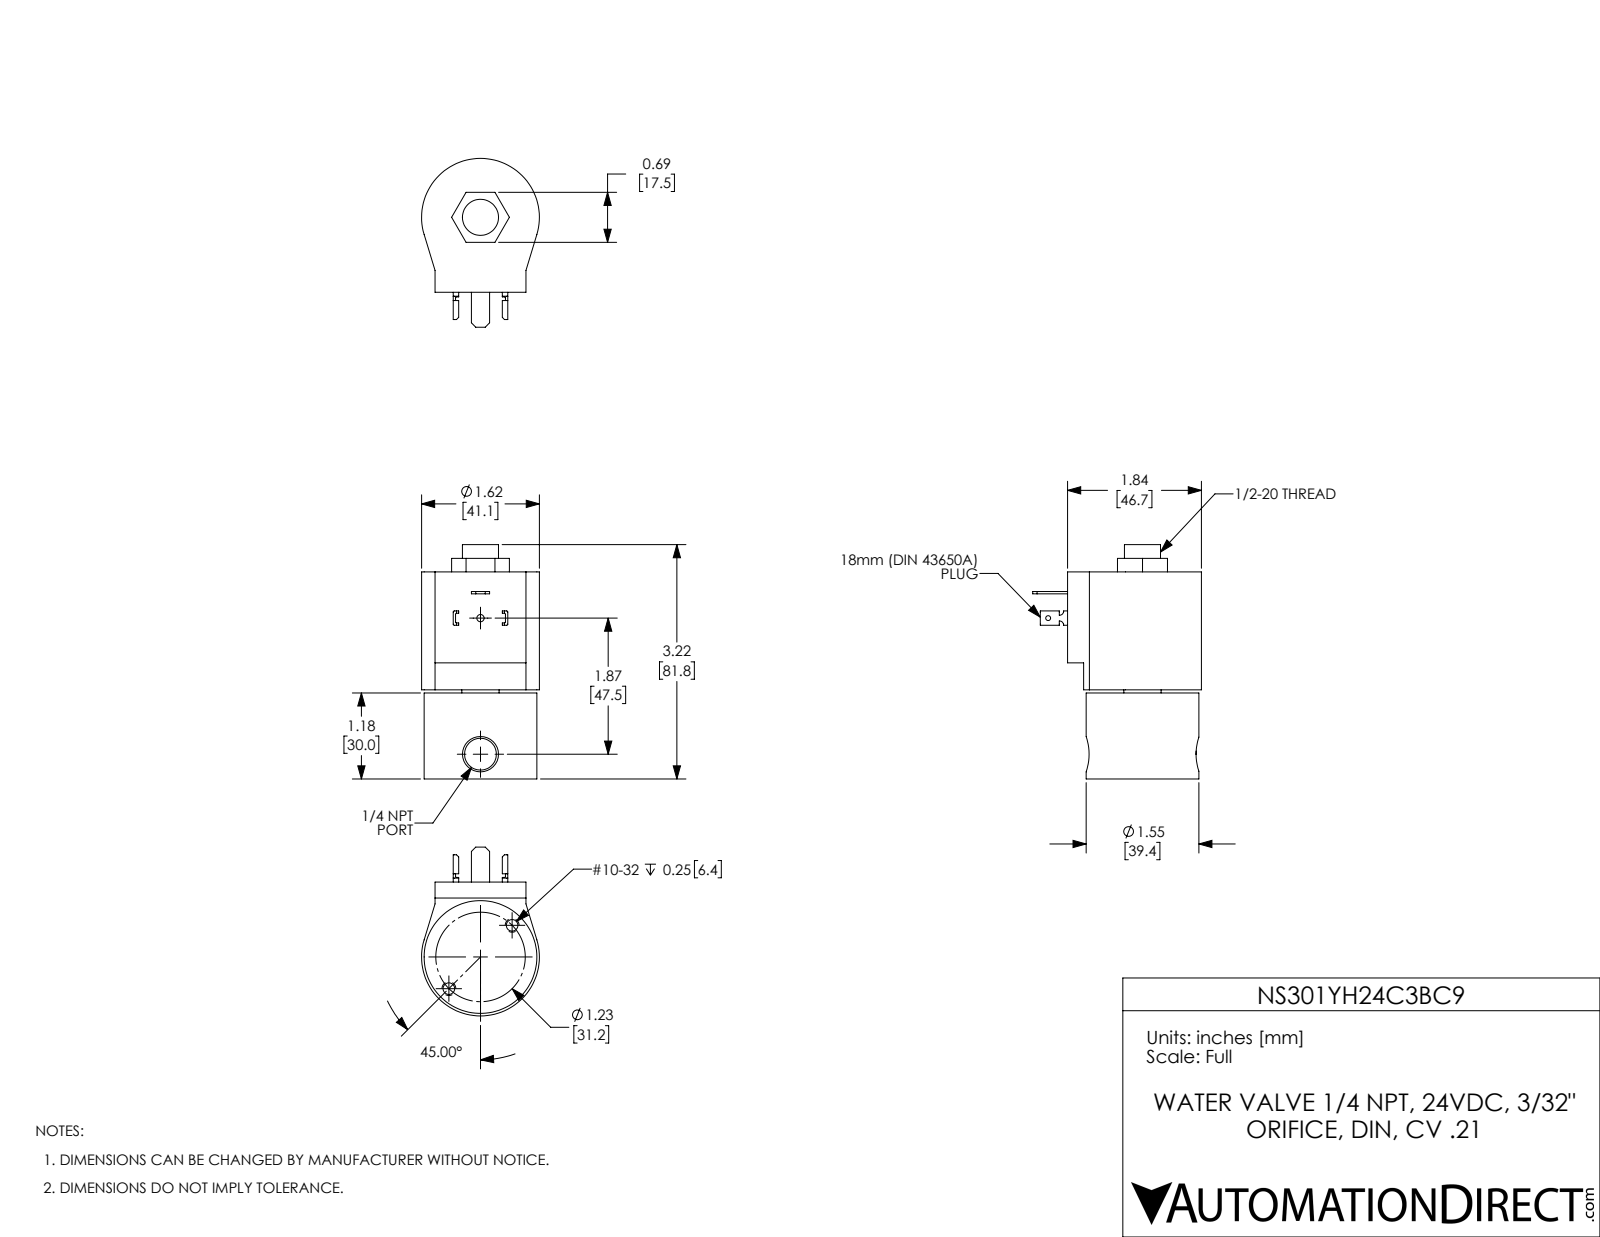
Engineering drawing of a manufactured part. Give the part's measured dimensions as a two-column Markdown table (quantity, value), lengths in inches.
| quantity | value |
| --- | --- |
| part name | NS301YH16C3BC9 |
| STEP written by | SolidWorks 2024 (CONFIG_CONTROL_DESIGN) |
| units | inches |
| bodies | 6 solids, 130 faces (73 planar, 49 cylindrical, 8 other) |
| overall size | 3.22 × 2.32 × 1.62 |
| volume | 6.042 in³ |
| surface area | 33.19 in² |
| round holes (diameter × count) | 0.159 × 2, 0.067 × 1, 0.1 × 1, 0.437 × 1, 0.496 × 1, 0.512 × 1, 1.155 × 1 |
| round bosses / shafts (diameter × count) | 1.55 × 1 |
| partial cylindrical surfaces (radius × count) | 0.015 × 8, 0.06 × 2, 0.81 × 1 |
| main face-to-face distances | 2.845, 1.182, 1.663, 1.225, 0.043, 1.62, 1.287, 0.106, 0.062, 1.558 |
| hole center spacings | 0.615, 1.23, 1.87 |
